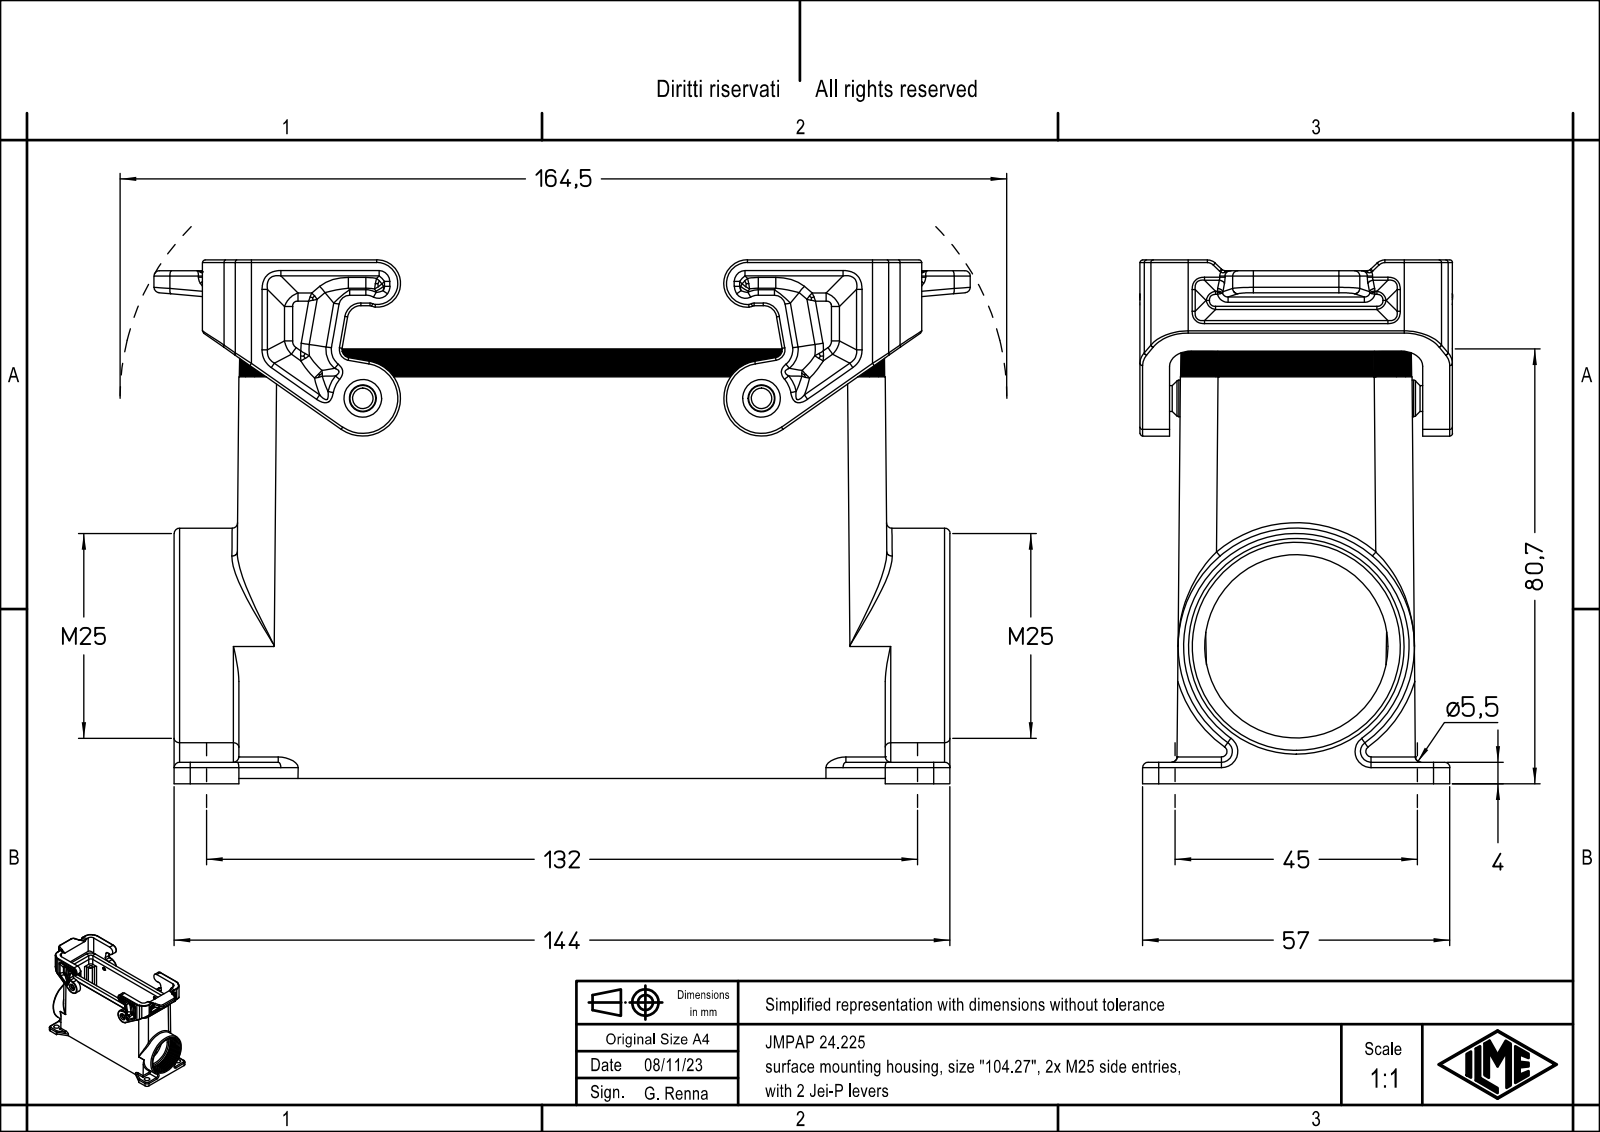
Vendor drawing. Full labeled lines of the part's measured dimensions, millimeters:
Part name (STEP PRODUCT): JMPAP 24.225
STEP written by: Creo Elements/Direct Modeling 20.1B 02-Apr-2019 (C) Parametric Technology GmbH (AUTOMOTIVE_DESIGN)
Units: millimetres
Bodies: 1 solid, 860 faces (170 planar, 310 cylindrical, 380 other)
Overall size (bounding box): 151.5 × 97.2 × 58.08
Volume: 192 617 mm³ · Surface area: 77 291 mm²
Round holes (diameter × count): ⌀3 ×4, ⌀3.5 ×4, ⌀5.5 ×4, ⌀4.8 ×2, ⌀23.6 ×1
Round bosses / shafts (diameter × count): ⌀6.8 ×2, ⌀43.87 ×1
Partial cylindrical surfaces — rounded edges, fillets, slot ends (radius × count): R0.5 ×50, R1 ×44, R3 ×38, R2 ×26, R1.5 ×12, R4 ×12, R6 ×12, R7 ×10
Main face-to-face distances: 3, 1, 4, 47, 10.25, 133.75, 144, 38.9, 7, 5.5
Hole centre spacings: 16.64, 38.63, 118.34, 123.37, 27, 45, 104, 107.45
